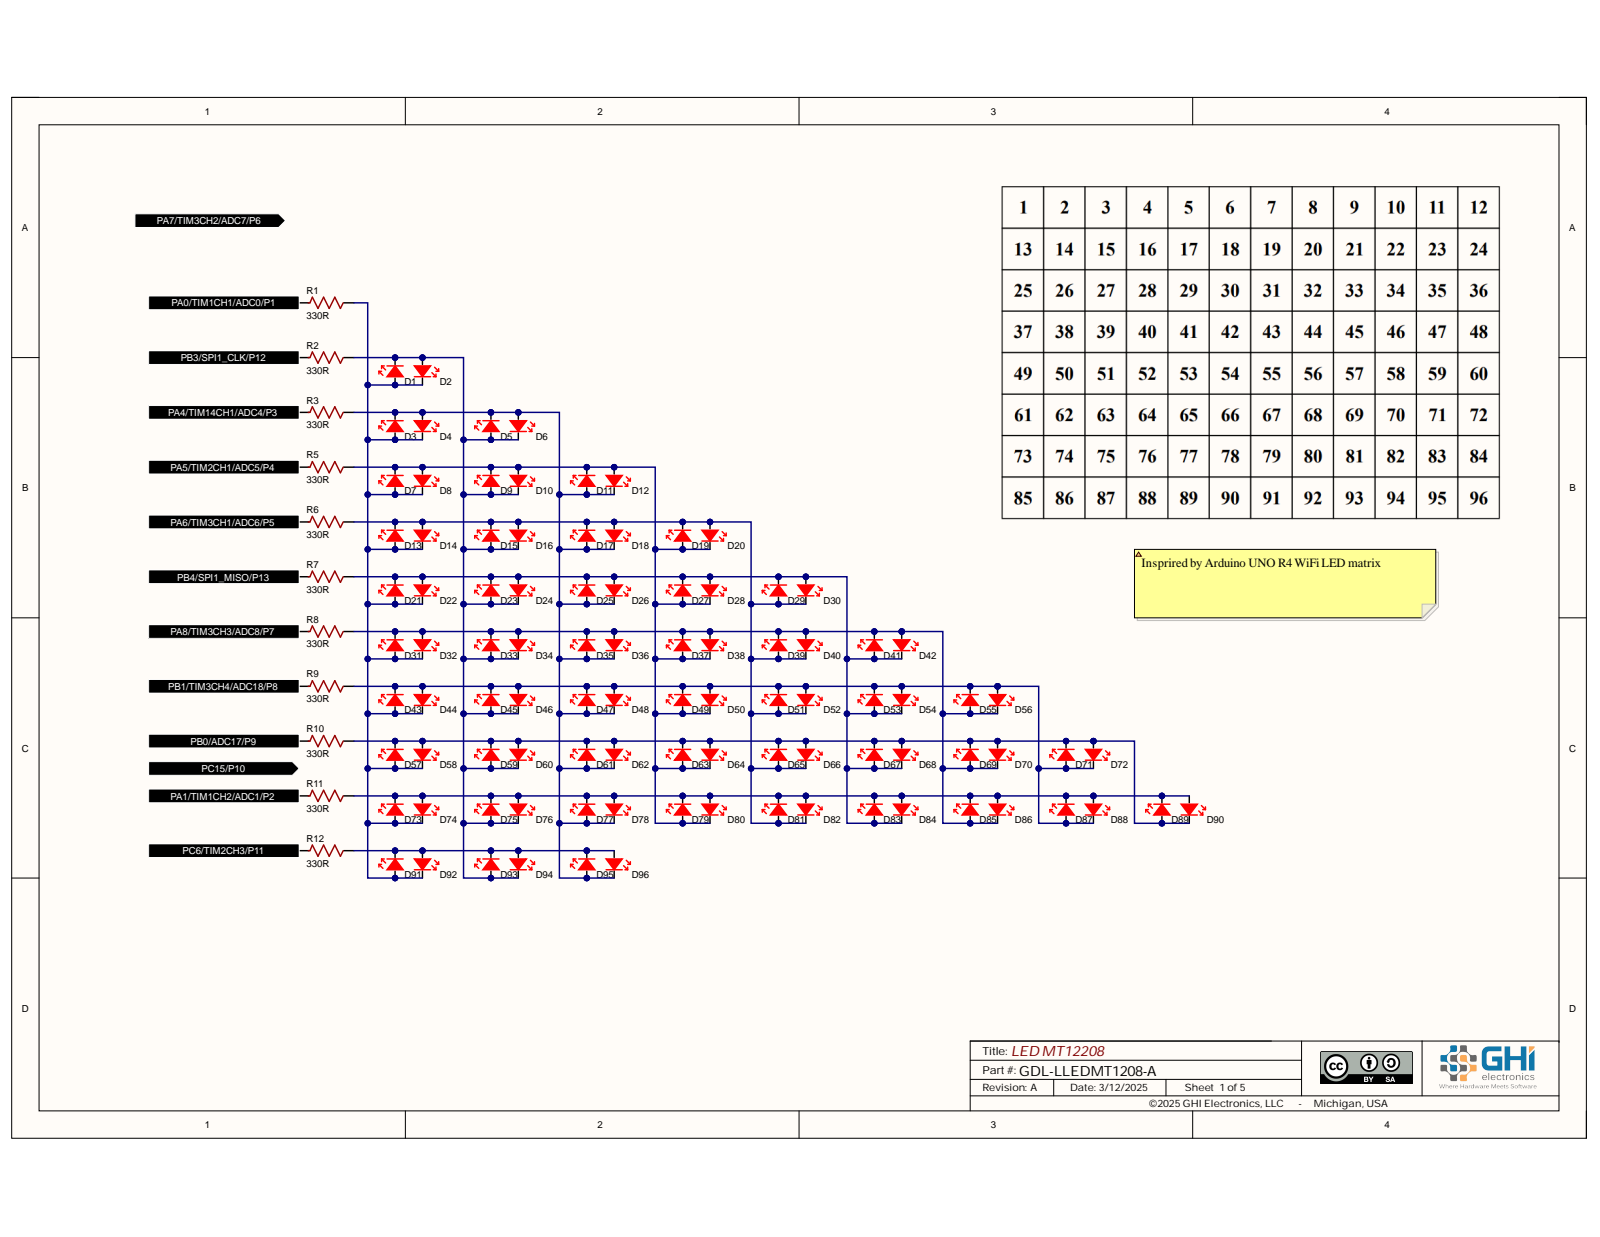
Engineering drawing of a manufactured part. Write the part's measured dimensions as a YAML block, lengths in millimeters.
part_name: "PCB; Board; STAT; 0603 LED Green (+5 more)"
step_written_by: "Open CASCADE 7.5 (AUTOMOTIVE_DESIGN)"
units: millimeters
bodies: {solids: 881, faces: 7669, planar: 6306, cylindrical: 1320, other: 43}
overall_size: [42, 32, 6.92]
volume: 2268
surface_area: 4593
round_holes:
  - {diameter: 3, count: 4}
  - {diameter: 1.02, count: 2}
partial_cylinders:
  - {radius: 0.17, count: 194}
  - {radius: 0.18, count: 194}
  - {radius: 0.18, count: 194}
  - {radius: 0.15, count: 78}
  - {radius: 0.12, count: 37}
  - {radius: 3.5, count: 4}
face_to_face_distances: [1.6, 1.9, 1.62, 1.77, 0.9, 7.07, 5.3, 0.6, 1.74, 0.87]
hole_center_spacings: [25, 35, 43.01, 2.54, 5.79, 8.31, 16.75, 19.29]
